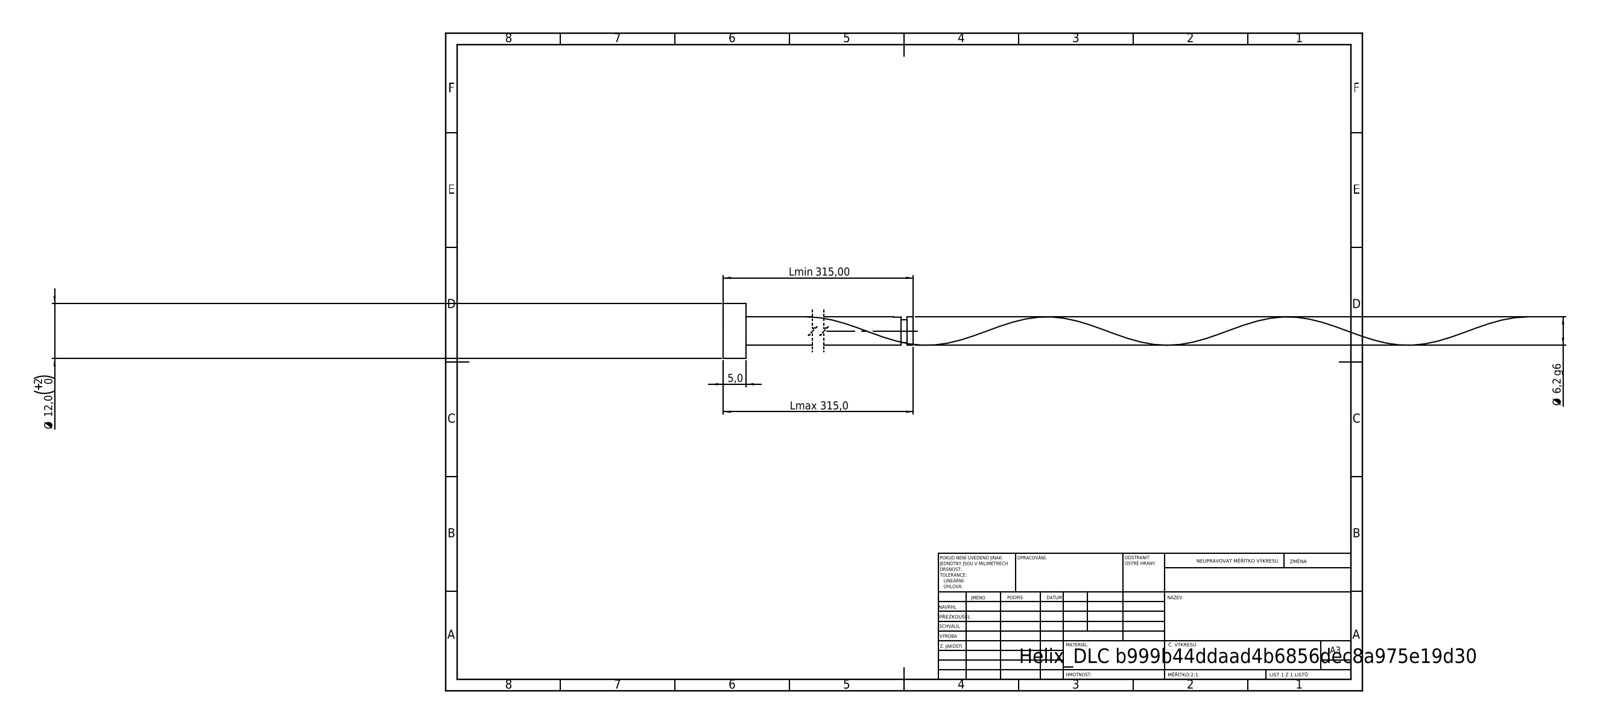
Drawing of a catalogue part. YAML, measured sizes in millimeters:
step_written_by: "SolidWorks 2019 (CONFIG_CONTROL_DESIGN)"
units: millimeters
bodies: {solids: 1, faces: 21, planar: 6, cylindrical: 14, other: 1}
overall_size: [315, 12, 12]
volume: 9820
surface_area: 6570
round_bosses_or_shafts:
  - {diameter: 12, count: 1}
  - {diameter: 6.2, count: 1}
  - {diameter: 4.96, count: 1}
face_to_face_distances: [5, 315, 310, 313.6, 308.6, 1.4, 312.36, 307.36, 1.24, 2.64]
